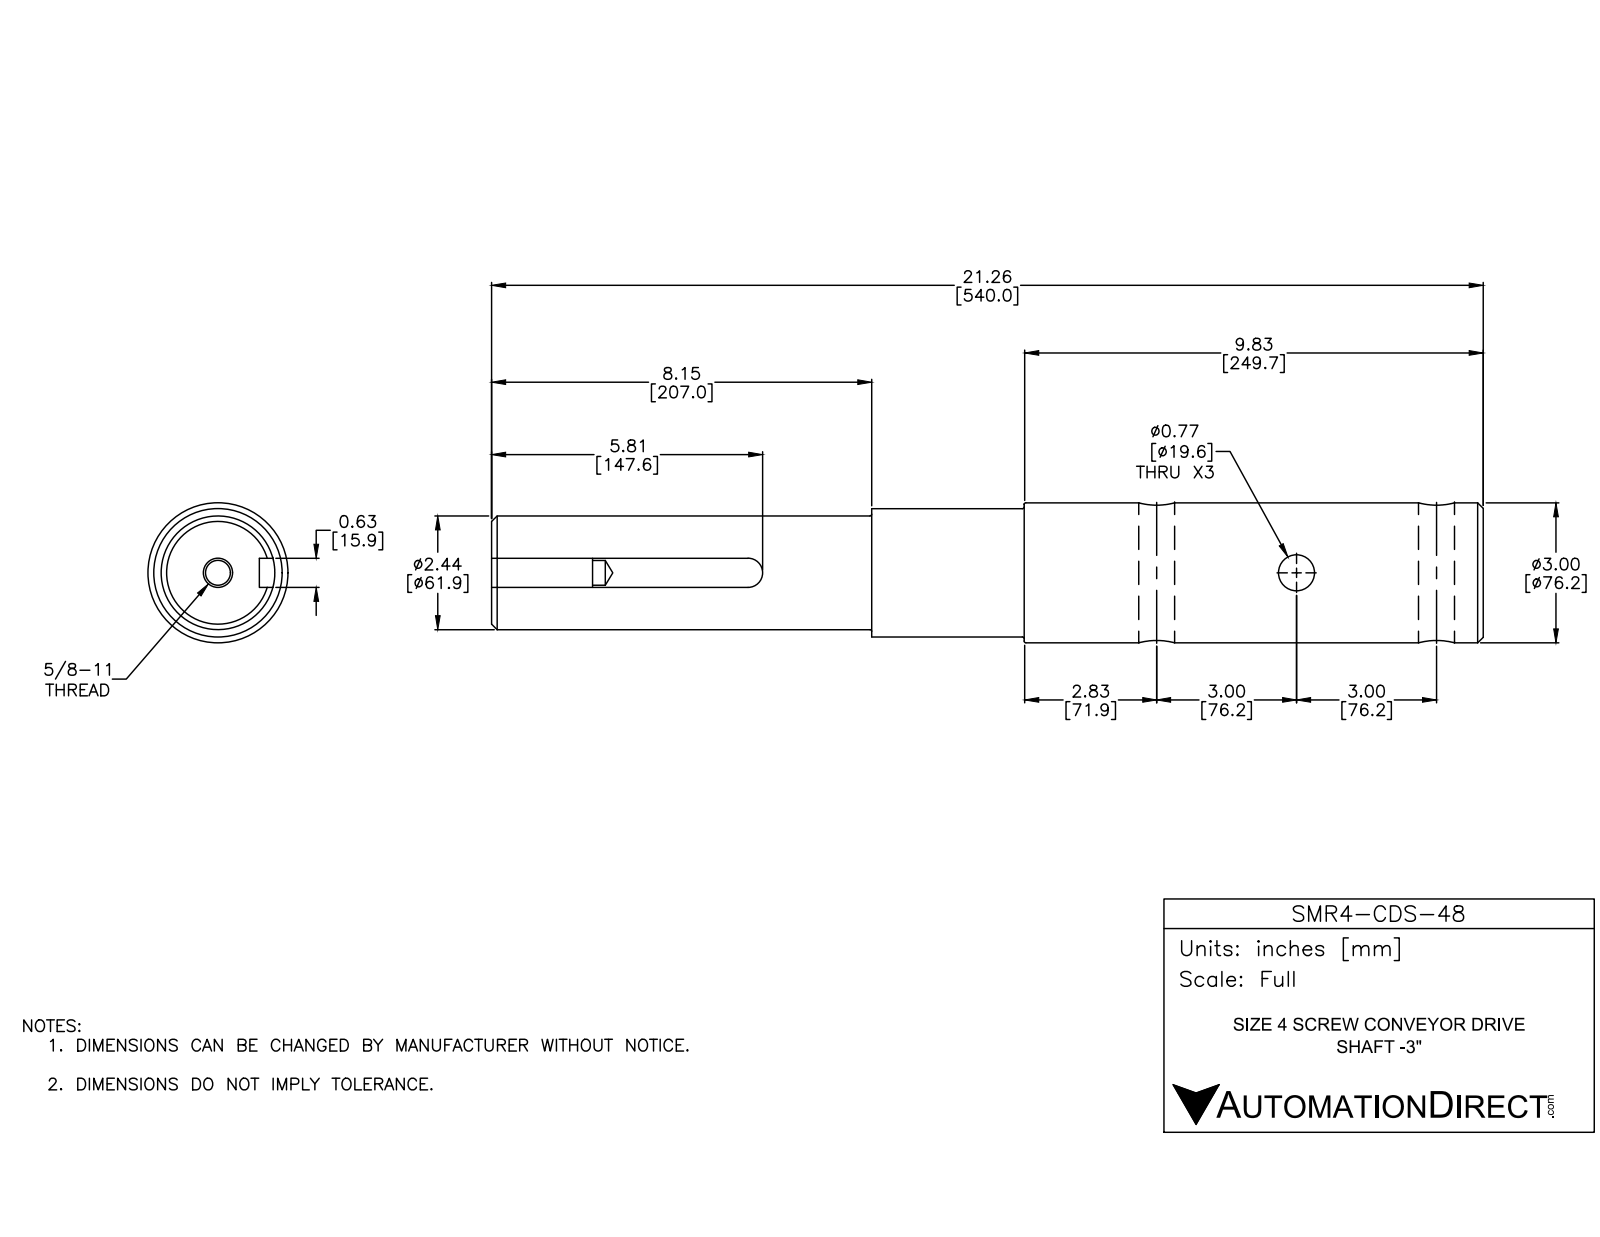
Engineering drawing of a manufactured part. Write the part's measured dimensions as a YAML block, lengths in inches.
part_name: "SMR4-CDS-48"
step_written_by: "SolidWorks 2016 (AUTOMOTIVE_DESIGN)"
units: inches
bodies: {solids: 1, faces: 38, planar: 8, cylindrical: 18, other: 12}
overall_size: [21.258, 3, 3]
volume: 120.8
surface_area: 222.5
round_holes:
  - {diameter: 0.772, count: 3}
  - {diameter: 0.531, count: 1}
  - {diameter: 0.625, count: 1}
round_bosses_or_shafts:
  - {diameter: 3, count: 1}
  - {diameter: 2.75, count: 1}
  - {diameter: 2.437, count: 1}
partial_cylinders:
  - {radius: 0.312, count: 1}
face_to_face_distances: [21.258, 0.625, 8.15, 13.108, 11.417, 3.268, 9.841, 2.165, 5.984, 9.252]
hole_center_spacings: [6]
